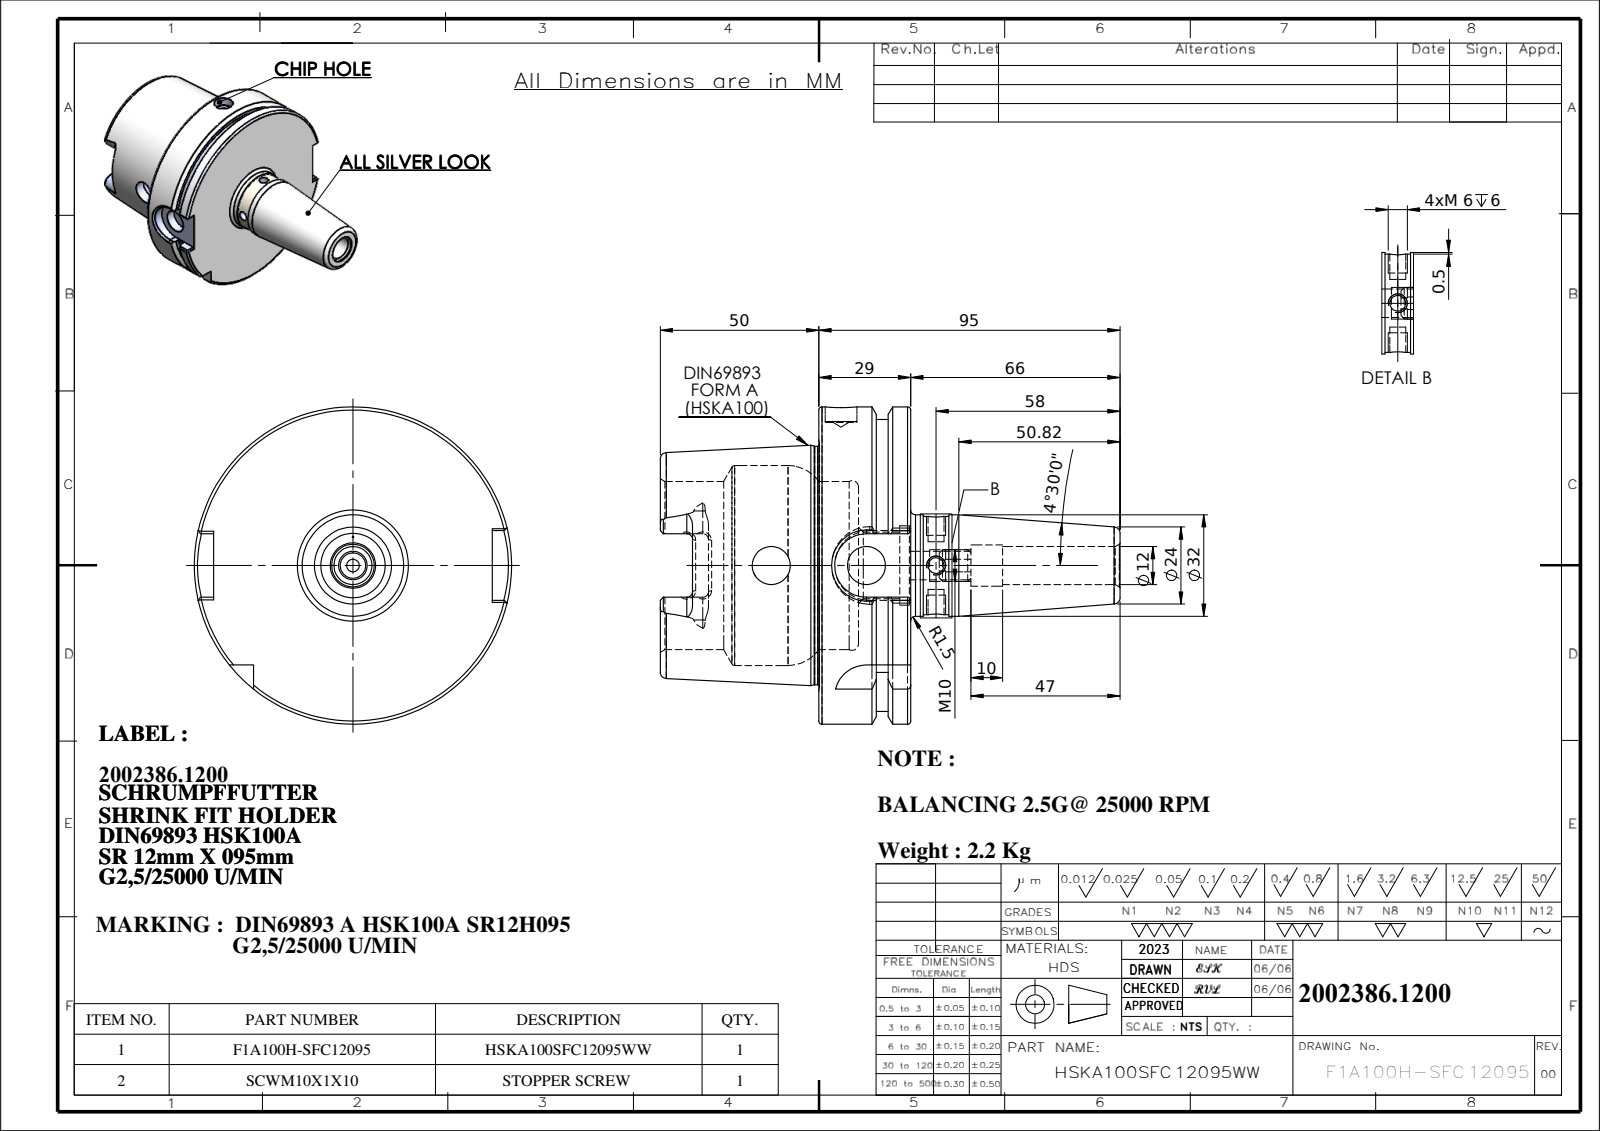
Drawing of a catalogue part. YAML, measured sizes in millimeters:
part_name: "91100A-SR12095; HSKA100SFC12095WW; SCWM10-10"
step_written_by: "SolidWorks 2018 (CONFIG_CONTROL_DESIGN)"
units: millimeters
bodies: {solids: 2, faces: 209, planar: 65, cylindrical: 68, other: 76}
overall_size: [144.95, 100, 100]
volume: 290264
surface_area: 58747
round_holes:
  - {diameter: 5, count: 2}
  - {diameter: 12, count: 2}
  - {diameter: 4, count: 1}
  - {diameter: 9, count: 1}
  - {diameter: 10, count: 1}
  - {diameter: 11.99, count: 1}
  - {diameter: 12.99, count: 1}
  - {diameter: 21, count: 1}
  - {diameter: 25, count: 1}
  - {diameter: 53, count: 1}
  - {diameter: 63, count: 1}
round_bosses_or_shafts:
  - {diameter: 100, count: 1}
  - {diameter: 92, count: 1}
  - {diameter: 75.16, count: 1}
  - {diameter: 32, count: 1}
  - {diameter: 31, count: 1}
  - {diameter: 10, count: 1}
partial_cylinders:
  - {radius: 1.8, count: 6}
  - {radius: 4.88, count: 4}
  - {radius: 10, count: 2}
  - {radius: 11, count: 1}
face_to_face_distances: [28.95, 12.5, 16.45, 50, 62.5, 78.95, 78.5, 28.5, 16, 0.45]
hole_center_spacings: [21.95, 29.95, 30, 51.95]
